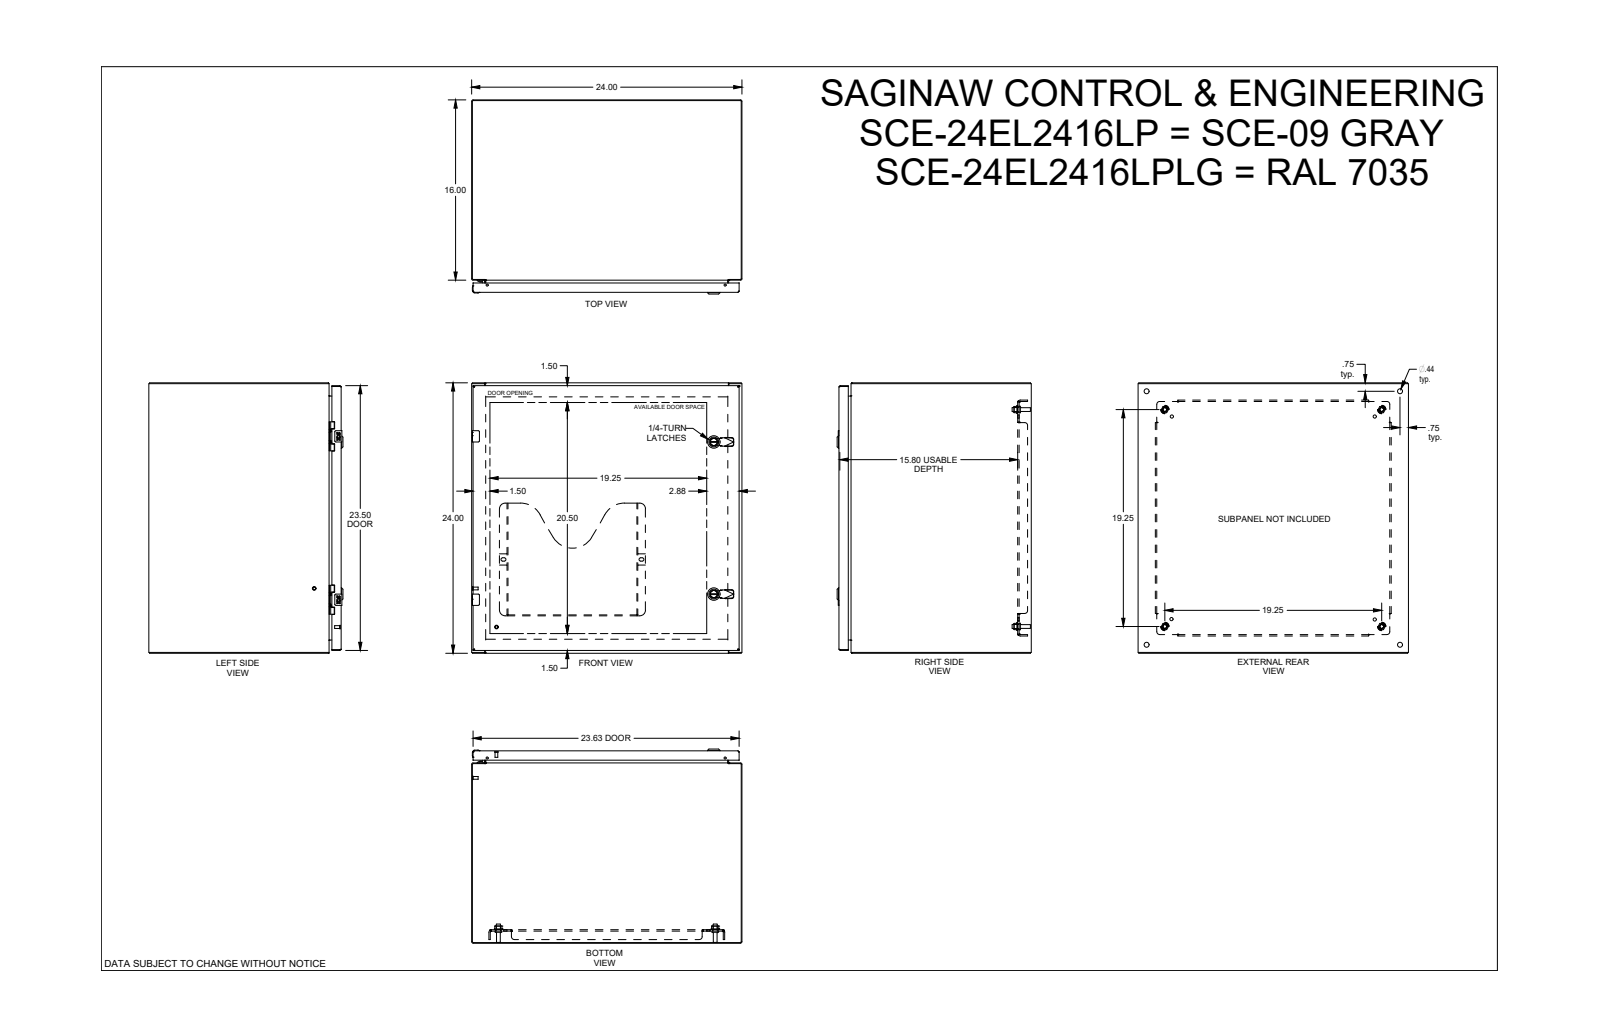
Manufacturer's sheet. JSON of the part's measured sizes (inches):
{"part_name": "SCE-24EL2416LP", "step_written_by": "SolidWorks 2021 (AUTOMOTIVE_DESIGN)", "units": "inches", "bodies": {"solids": 45, "faces": 2823, "planar": 1099, "cylindrical": 854, "other": 870}, "overall_size": [24, 24, 17.23], "volume_in3": 297.1, "surface_area_in2": 7303, "round_holes": [[0.172, 4], [0.205, 4], [0.244, 4], [0.266, 4], [0.281, 4], [0.367, 4], [0.375, 4], [0.437, 4], [0.5, 4], [0.04, 2], [0.188, 2], [0.197, 2]], "round_bosses_or_shafts": [[0.17, 6], [0.366, 4], [0.332, 4], [0.25, 4], [0.248, 4], [0.24, 4], [0.196, 3], [1.102, 2]], "partial_cylinders_radius": [[0.012, 56], [0.01, 28], [0.015, 24], [0.02, 20], [0.04, 17], [0.06, 13], [0.029, 12], [0.1, 12]], "face_to_face_distances": [0.075, 23.925, 23.85, 24, 0.06, 17.073, 16.998, 17.013, 16.938, 1.2], "hole_center_spacings": [20.938, 0.985, 14.5, 18.641, 20.38, 0.02, 0.493, 0.494]}
